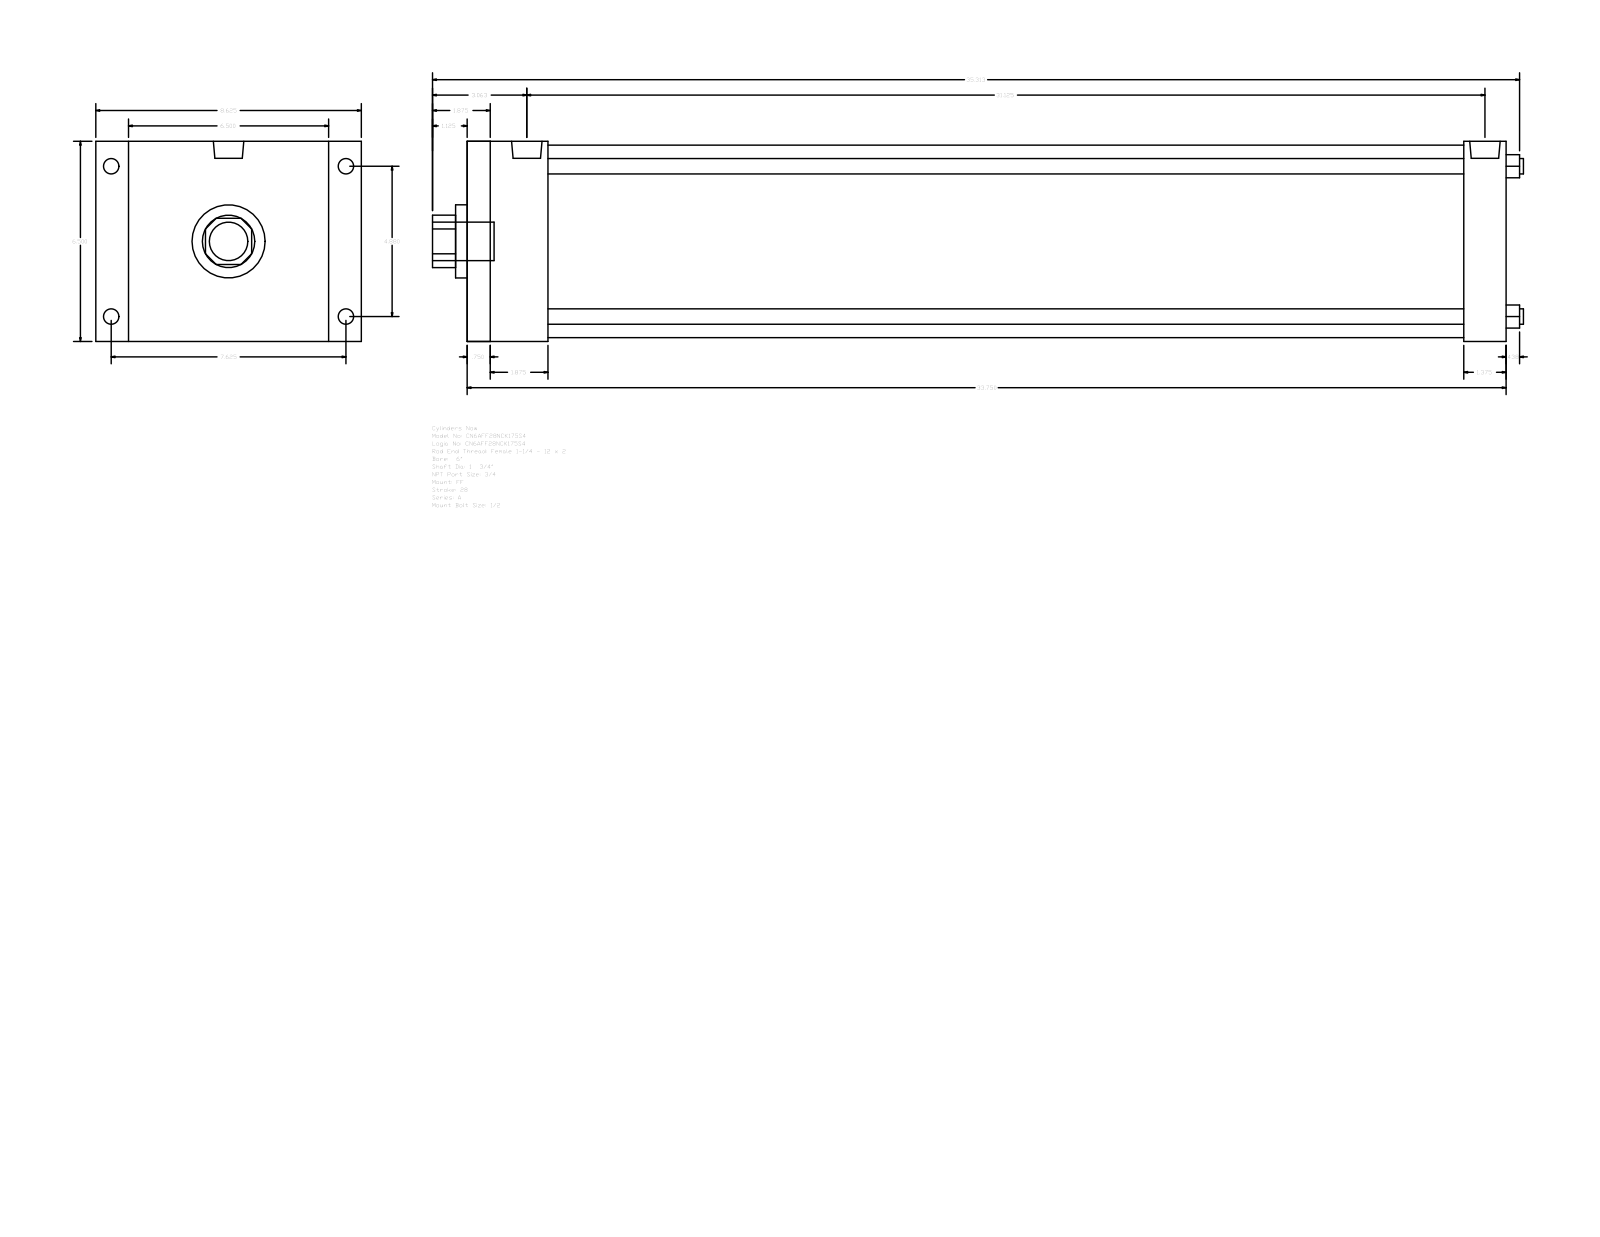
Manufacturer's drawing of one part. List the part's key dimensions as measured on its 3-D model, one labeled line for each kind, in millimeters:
Part name (STEP PRODUCT): A_FF__0600_1.75
STEP written by: GSSL Pune (CONFIG_CONTROL_DESIGN)
Units: millimetres
Bodies: 0 solids, 92 faces (64 planar, 28 cylindrical, 0 other)
Overall size (bounding box): 900.11 × 219.07 × 165.1
Round holes (diameter × count): ⌀12.7 ×4, ⌀44.45 ×1, ⌀60.33 ×1, ⌀158.75 ×1
Round bosses / shafts (diameter × count): ⌀15.08 ×4, ⌀12.7 ×4, ⌀25.12 ×2, ⌀31.75 ×1
Partial cylindrical surfaces — rounded edges, fillets, slot ends (radius × count): R21.63 ×1
Main face-to-face distances: 165.1, 857.26, 19.05, 838.21, 66.68, 47.63, 790.58, 822.33, 803.28, 755.65
Hole centre spacings: 87.65, 123.96, 175.31
